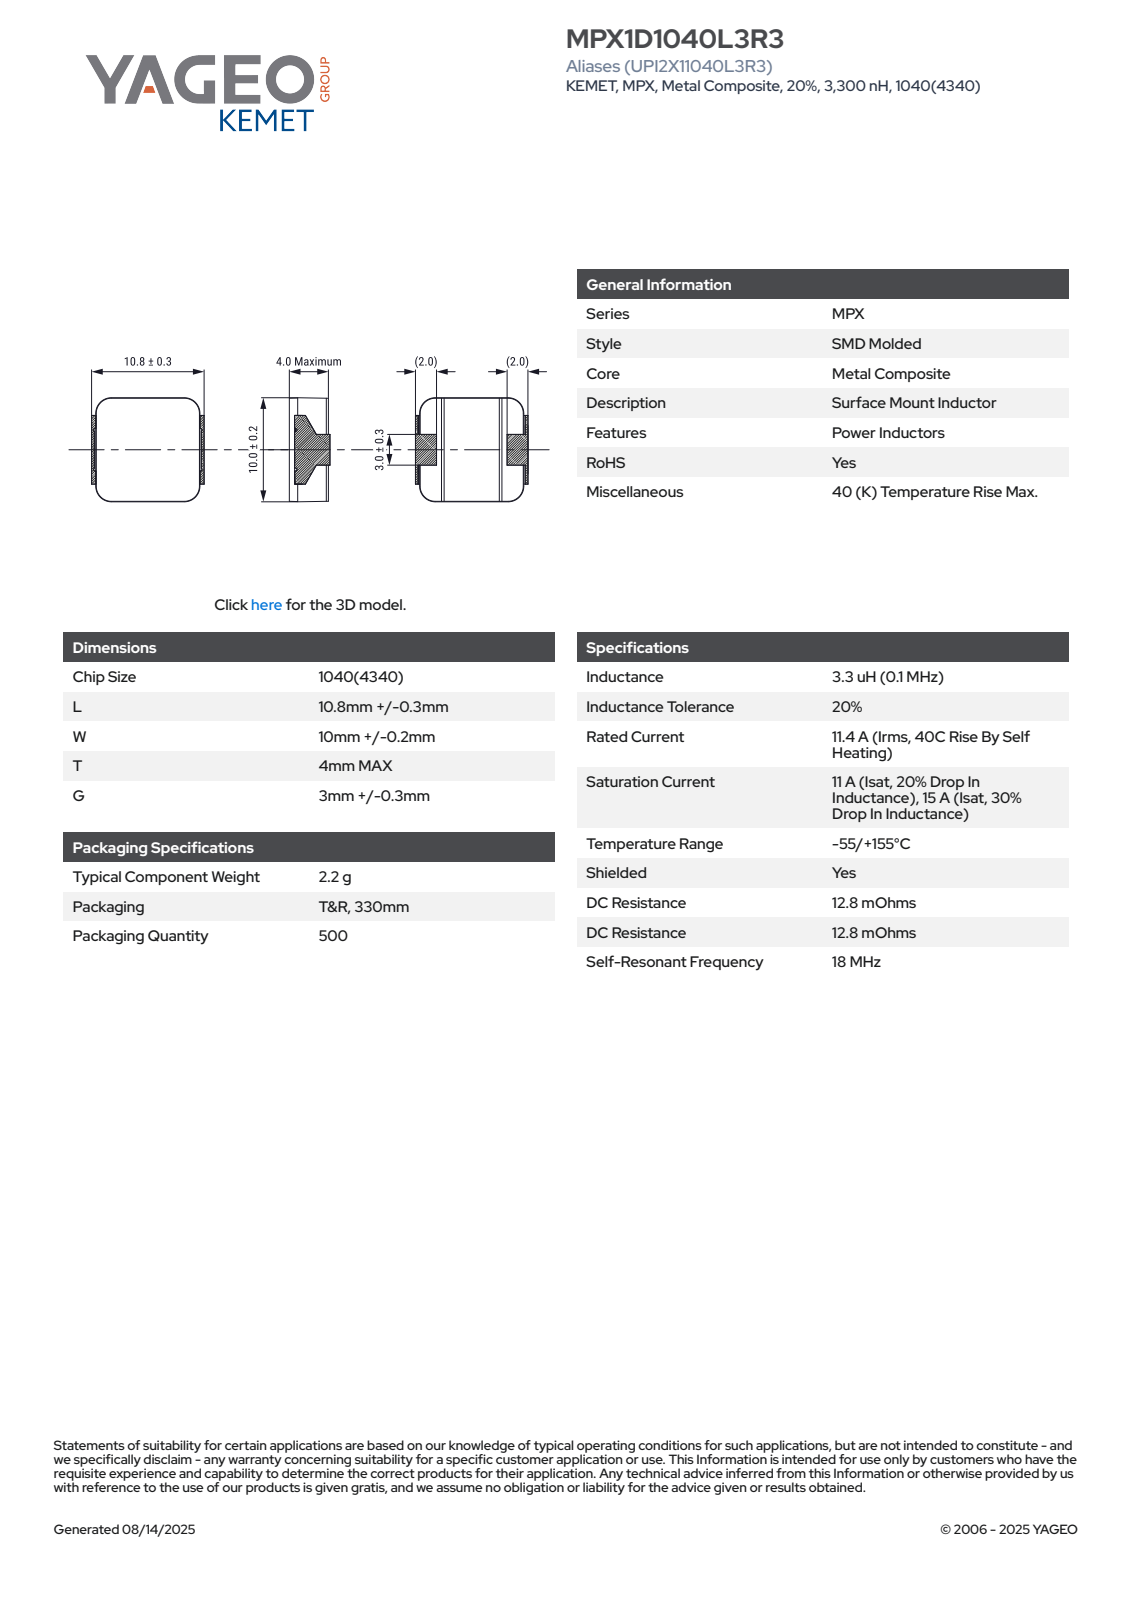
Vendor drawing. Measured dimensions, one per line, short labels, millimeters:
name: MPX1D1040(3)(KEMET
written by: SolidWorks 2018 (AUTOMOTIVE_DESIGN)
unit: mm
bodies: 1 solid, 131 faces (112 planar, 19 cylindrical, 0 other)
size: 11.1 × 10.2 × 4.06
volume: 407 mm³; area: 426 mm²
rounds: 4× R0.26, 4× R1.45, 4× R1.5, 3× R0.15
face distances: 4, 3.8, 10.84, 10.58, 11.1, 4.06, 3.05, 3.16, 3.1, 2.9
